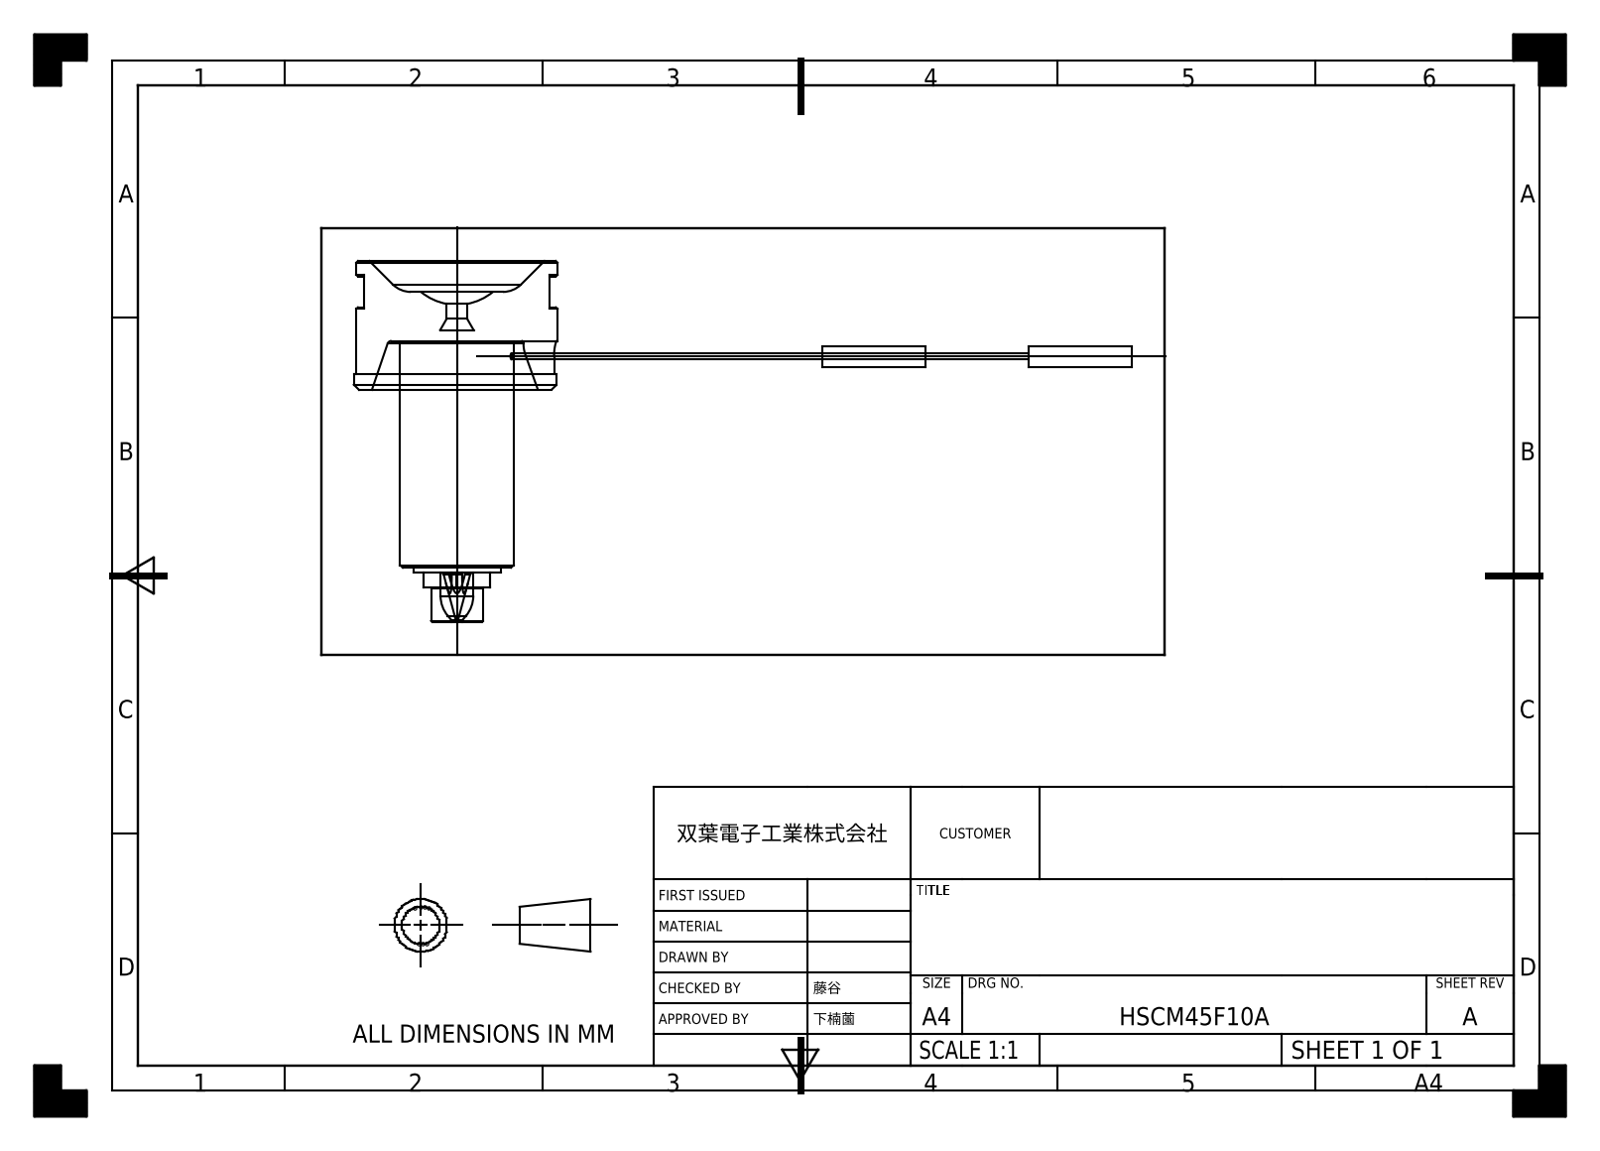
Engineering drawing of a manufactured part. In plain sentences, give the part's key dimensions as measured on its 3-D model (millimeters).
The part is named "HSCM45F10A". Its 3-D file was written by "SIEMENS PLM Software NX 2023 (AUTOMOTIVE_DESIGN)". It is 1 solid with 74 faces: 30 planar, 23 cylindrical and 21 other. Overall it measures 151 by 70 by 40 millimeters. Its volume is 37 121 cubic millimeters and its surface area 11 223 square millimeters. Round holes: 1 of diameter 2, 1 of diameter 4, 1 of diameter 6.35. Round bosses or shafts: 2 of diameter 4, 2 of diameter 1.2, 1 of diameter 40, 1 of diameter 39, 1 of diameter 22, 1 of diameter 16.9, 1 of diameter 10. Partial cylindrical surfaces (rounded edges, fillets, slot ends): 3 of radius 2.8, 2 of radius 3, 1 of radius 7.45. The main face-to-face distances are 9.5, 25, 54.5, 45, 15.5, 59.5, 44, 34.5, 3, 6.
